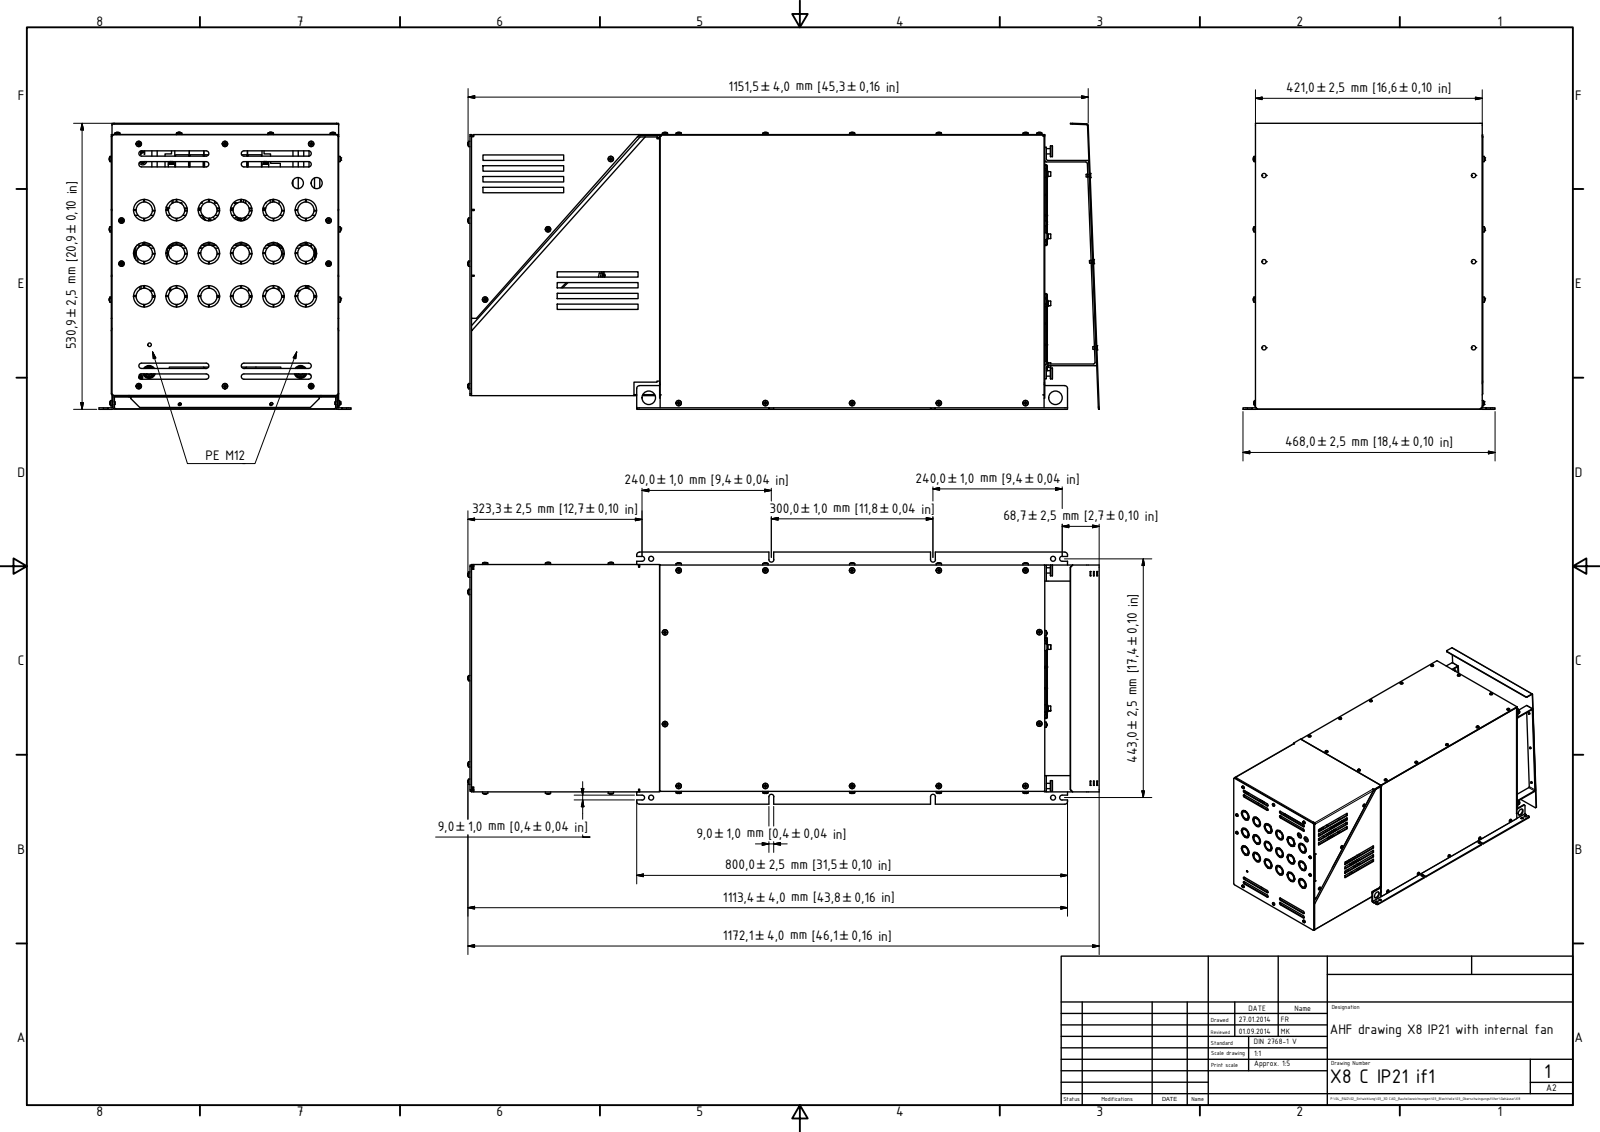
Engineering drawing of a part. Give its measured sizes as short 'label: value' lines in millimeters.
name: 10100531 Seitenwand X8-A1; 10100530 Lüfterblech X8-A1; 10100529 Anschlussblech X8-A1; 10100404 Deckel X7-X8 (+8 more)
written by: Autodesk Inventor 2015 (AUTOMOTIVE_DESIGN)
unit: mm
bodies: 181 solids, 11822 faces (7290 planar, 2646 cylindrical, 1886 other)
size: 1172.13 × 530.87 × 468
volume: 8 990 000 mm³; area: 7 725 000 mm²
holes: 49× ⌀4.13, 47× ⌀6.5, 28× ⌀7, 21× ⌀4, 20× ⌀3.24, 18× ⌀40, 14× ⌀6, 10× ⌀5, 6× ⌀9, 6× ⌀10, 6× ⌀14, 4× ⌀3.95
bosses: 51× ⌀5, 46× ⌀4.6, 16× ⌀1.4, 14× ⌀16, 14× ⌀8.5, 12× ⌀30, 12× ⌀26.7, 8× ⌀10
rounds: 136× R0.83, 135× R1, 115× R0.15, 71× R0.5, 71× R2, 65× R3.25, 64× R0.31, 61× R0.1
face distances: 1, 2, 419, 420, 418, 3, 714, 421, 482.6, 1.5
hole spacings: 100, 161, 389, 7.5, 21, 200, 322, 400
